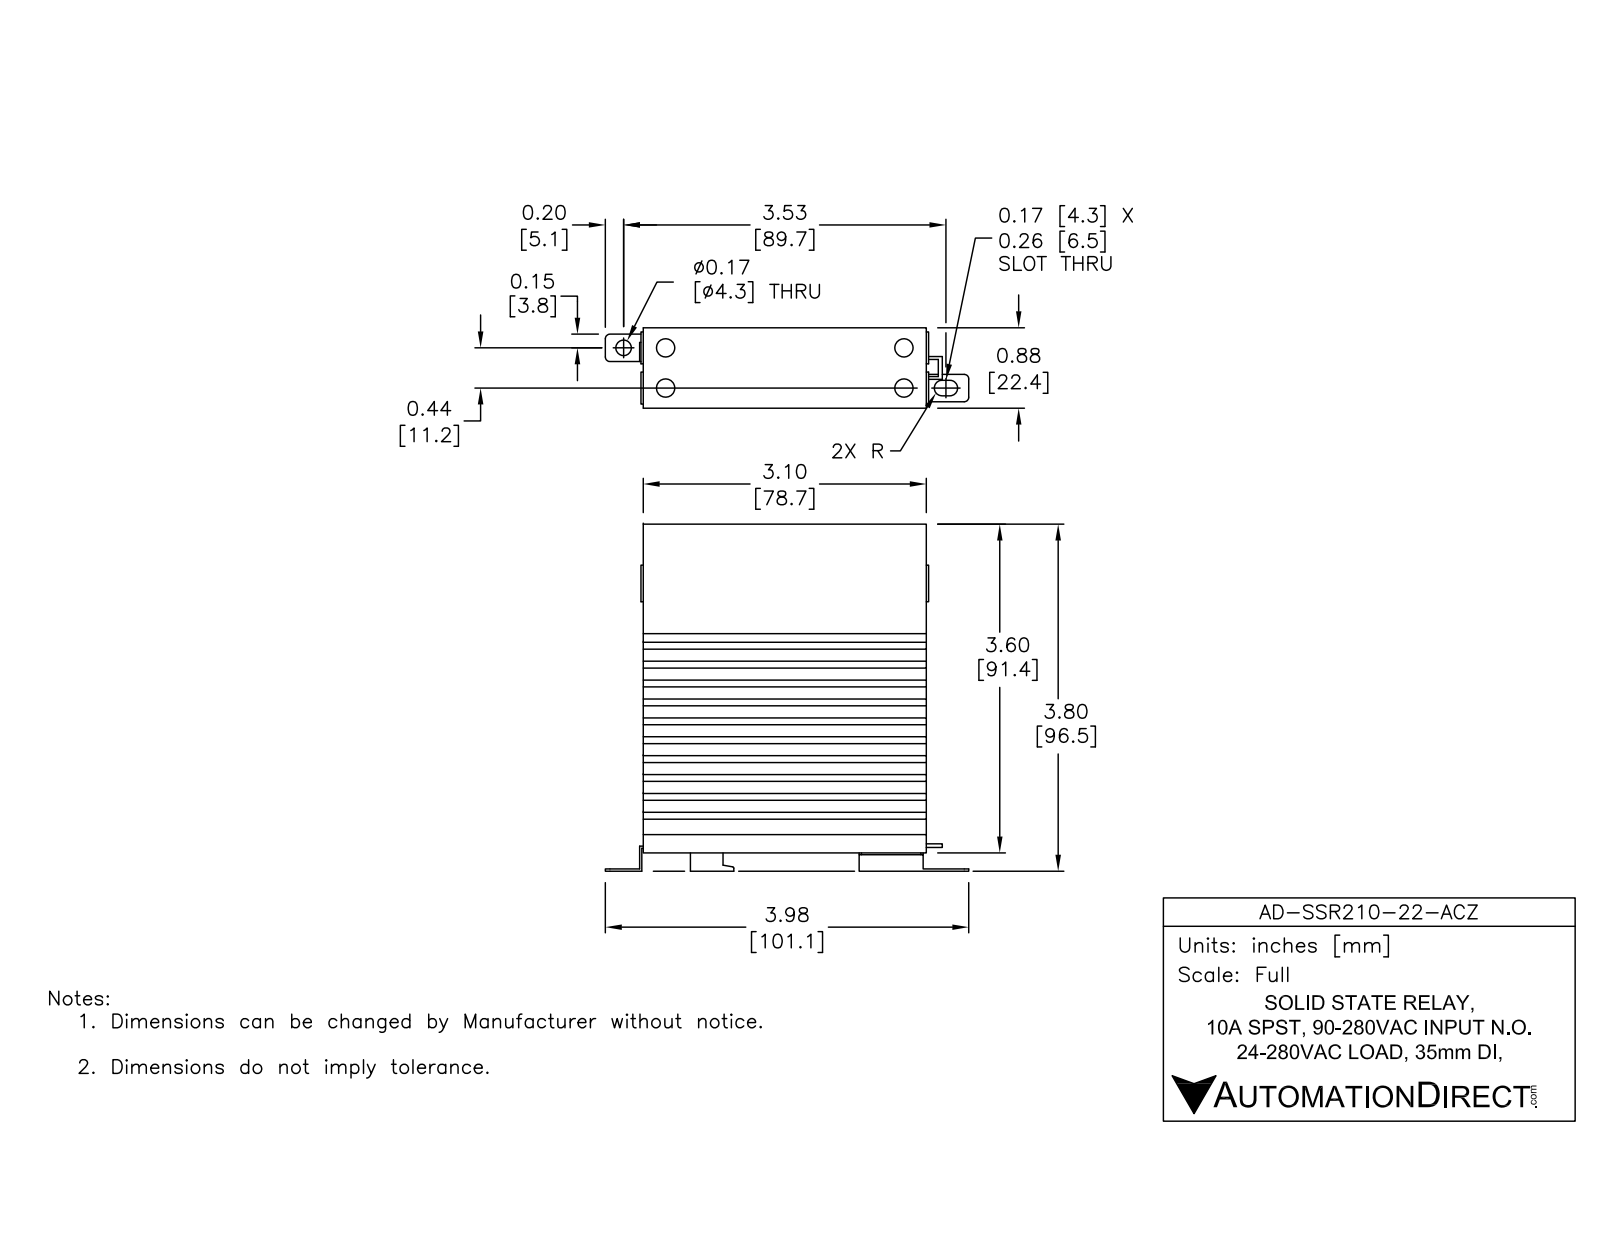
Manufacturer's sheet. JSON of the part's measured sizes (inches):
{"part_name": "AD-SSR210-22-ACZ", "step_written_by": "SolidWorks 2014 (AUTOMOTIVE_DESIGN)", "units": "inches", "bodies": {"solids": 1, "faces": 215, "planar": 195, "cylindrical": 20, "other": 0}, "overall_size": [3.98, 3.8, 0.88], "volume_in3": 7.136, "surface_area_in2": 74.91, "round_holes": [[0.2, 4], [0.17, 1]], "partial_cylinders_radius": [[0.05, 6], [0.085, 2], [0.015, 1]], "face_to_face_distances": [0.62, 0.207, 0.827, 0.414, 0.132, 0.489, 0.339, 0.413, 0.075, 0.207], "hole_center_spacings": [0.44, 2.61, 2.647, 0.46, 0.637, 3.07, 3.102]}
